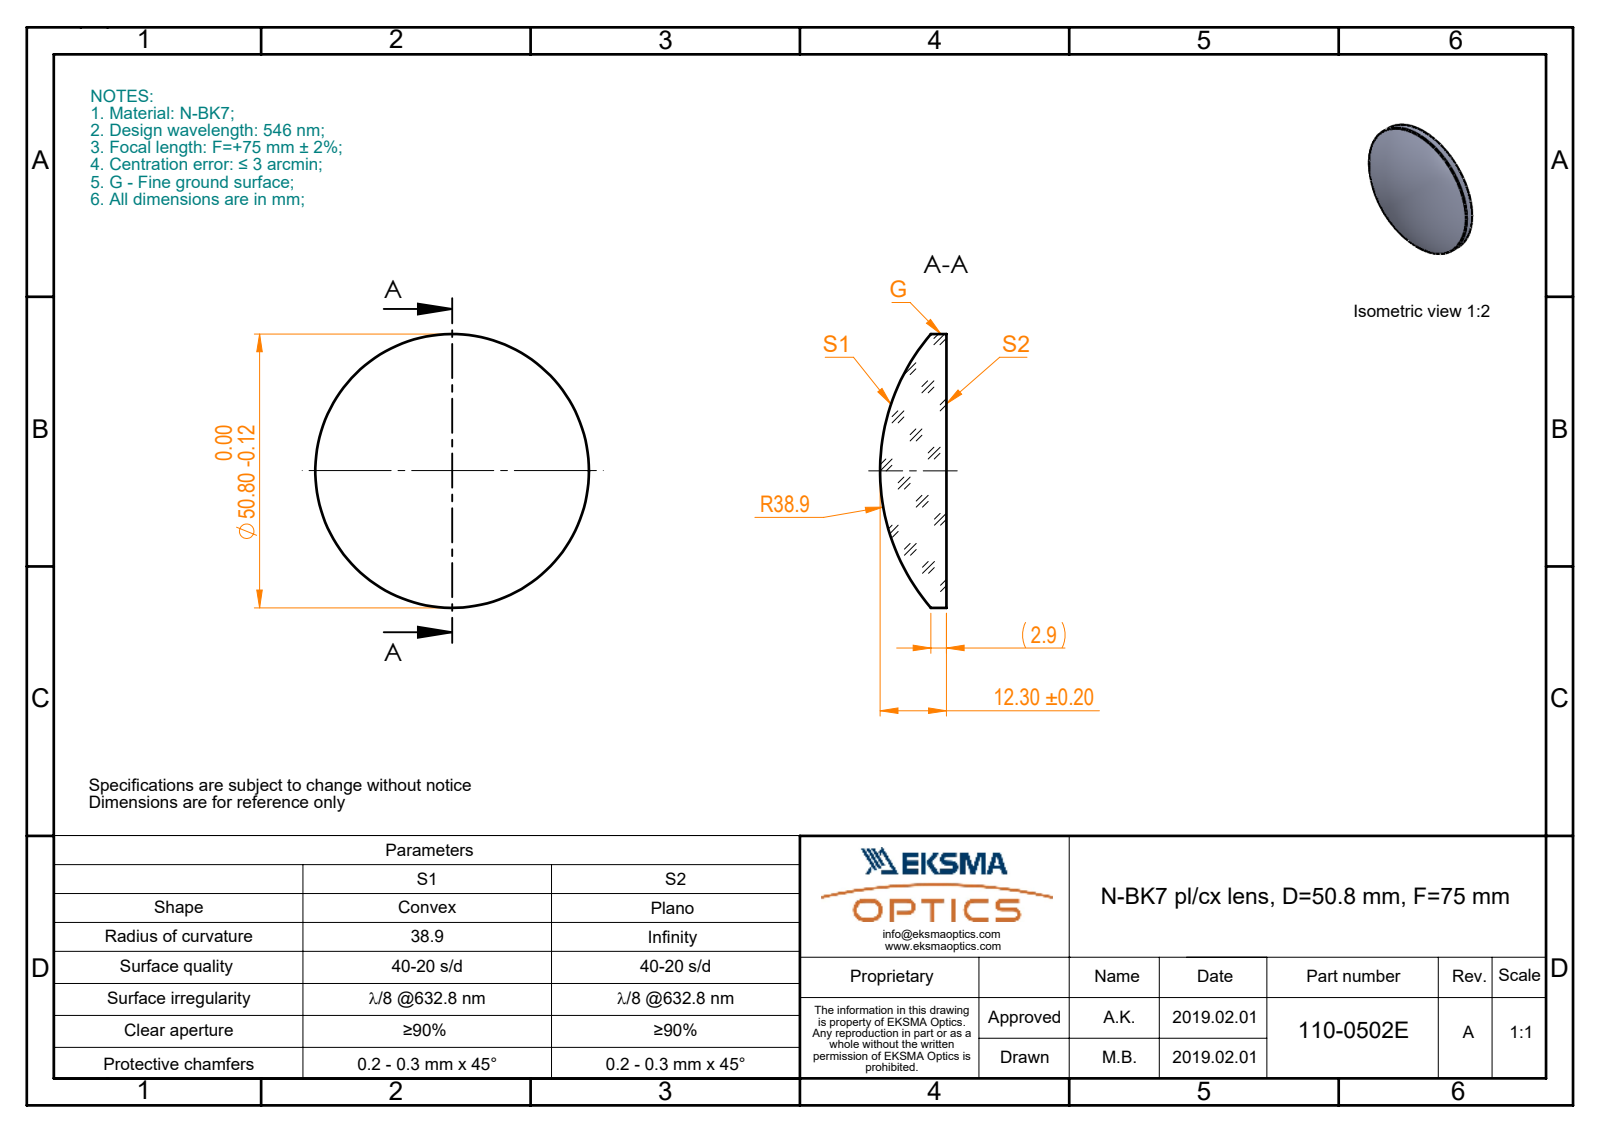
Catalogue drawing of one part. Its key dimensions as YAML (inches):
part_name: "110-0502E BK7 pl-cx 50.8 F75"
step_written_by: "SolidWorks 2017 (CONFIG_CONTROL_DESIGN)"
units: inches
bodies: {solids: 1, faces: 5, planar: 1, cylindrical: 2, other: 2}
overall_size: [2, 2, 0.484]
volume: 0.965
surface_area: 7.425
round_bosses_or_shafts:
  - {diameter: 2, count: 1}
